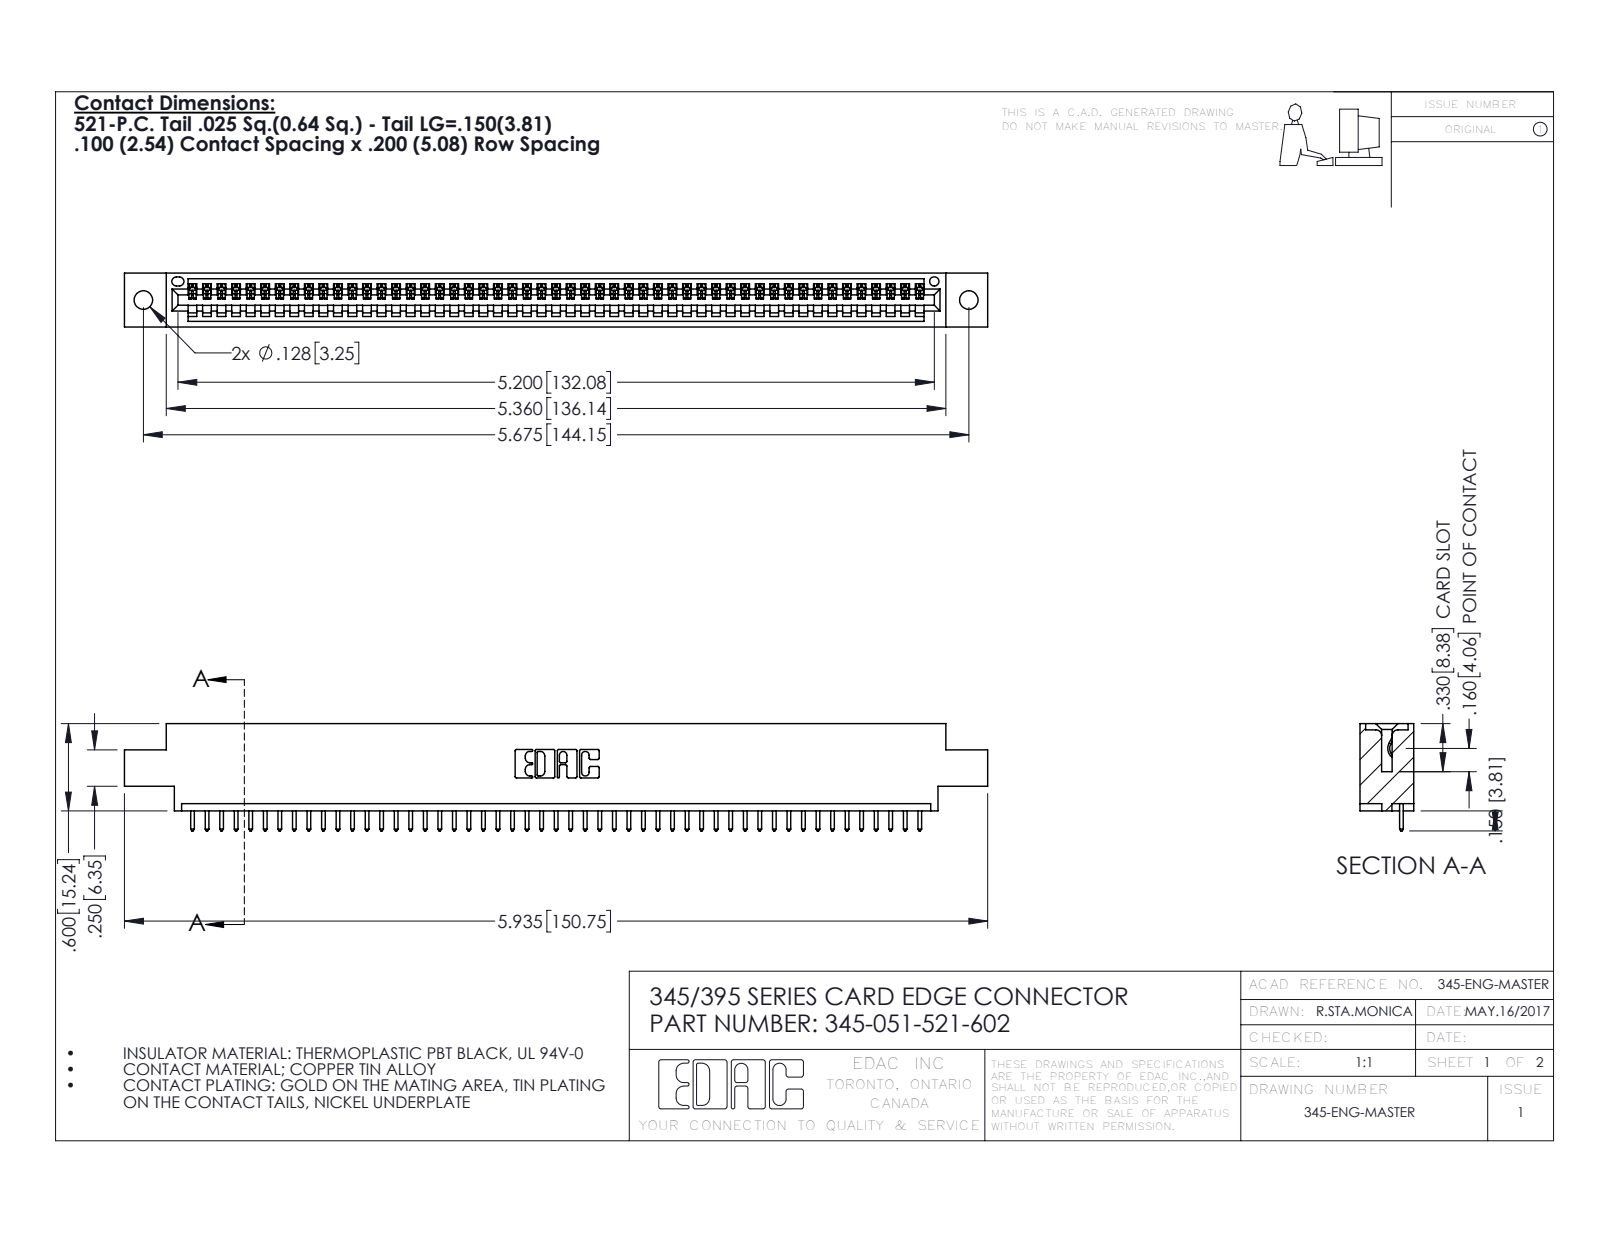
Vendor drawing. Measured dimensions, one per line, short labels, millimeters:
name: 345 Part_0.170 Offset - 0.128 Dia; 345-292-001_345-293-121; 345-051-521-602
written by: SolidWorks 2016 (CONFIG_CONTROL_DESIGN)
unit: mm
bodies: 52 solids, 3088 faces (2124 planar, 964 cylindrical, 0 other)
size: 150.7 × 18.7 × 9.4
volume: 14 100 mm³; area: 18 140 mm²
holes: 2× ⌀3.3, 1× ⌀1.6
rounds: 102× R0.2, 102× R0.3, 22× R0.3, 6× R0.2, 6× R0.8, 3× R0.7, 2× R0.8, 2× R1
face distances: 7.6, 1.8, 9.4, 5.1, 2.5, 6.9, 0.6, 5.7, 4.4, 3.8
hole spacings: 6.9, 138.2, 144.1
